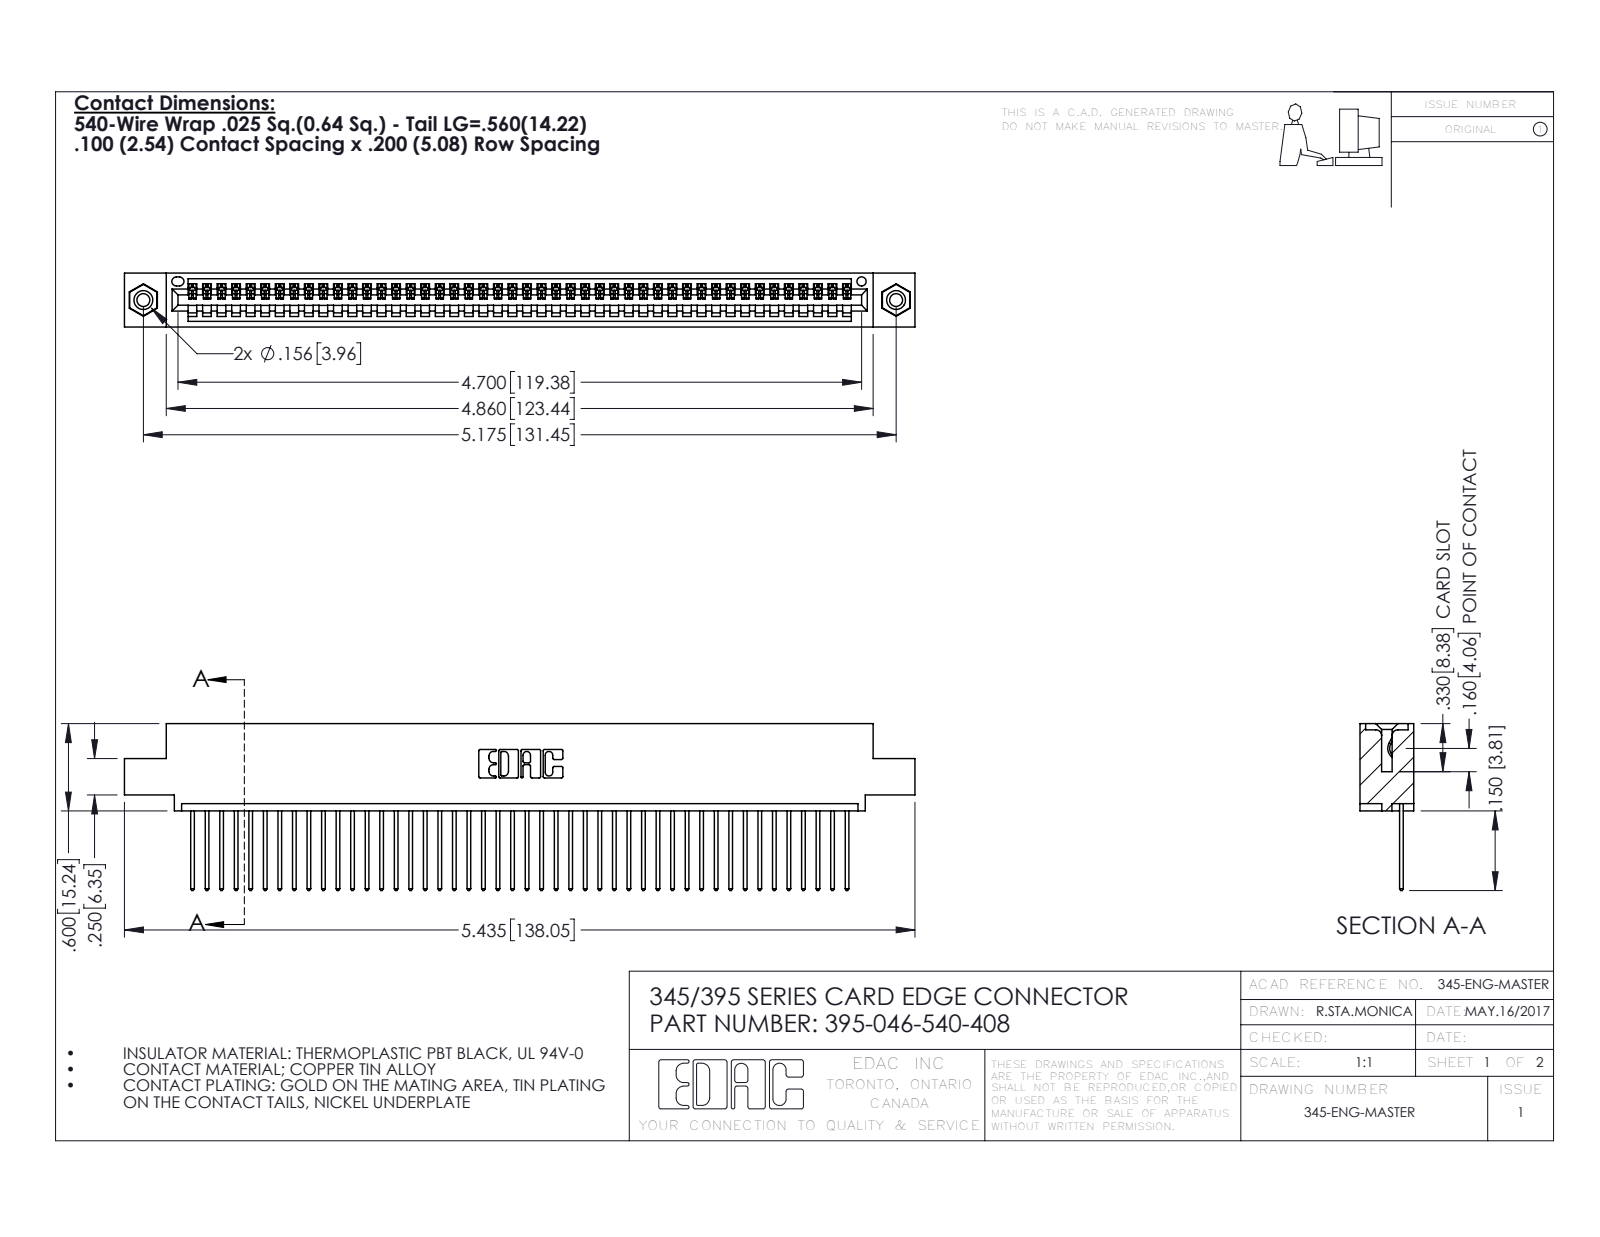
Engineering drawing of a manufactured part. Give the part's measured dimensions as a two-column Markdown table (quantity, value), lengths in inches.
| quantity | value |
| --- | --- |
| part name | 345-250-001_345-250-003-102; 395-046-540-408; 345 Part_0.110 Offset - 0.156 Dia-TI; 345-292-001_345-293-140 |
| STEP written by | SolidWorks 2016 (CONFIG_CONTROL_DESIGN) |
| units | inches |
| bodies | 49 solids, 2858 faces (1956 planar, 886 cylindrical, 16 other) |
| overall size | 5.435 × 1.147 × 0.37 |
| volume | 0.801 in³ |
| surface area | 27.98 in² |
| round holes (diameter × count) | 0.089 × 2, 0.125 × 2, 0.156 × 2, 0.064 × 1 |
| round bosses / shafts (diameter × count) | 0.155 × 2 |
| partial cylindrical surfaces (radius × count) | 0.006 × 92, 0.01 × 92, 0.01 × 22, 0.007 × 6, 0.031 × 6, 0.026 × 3, 0.031 × 2, 0.04 × 2 |
| main face-to-face distances | 0.072, 0.298, 0.37, 0.098, 0.272, 0.025, 0.2, 0.225, 0.149, 0.072 |
| hole center spacings | 0.27, 4.939, 5.175 |
